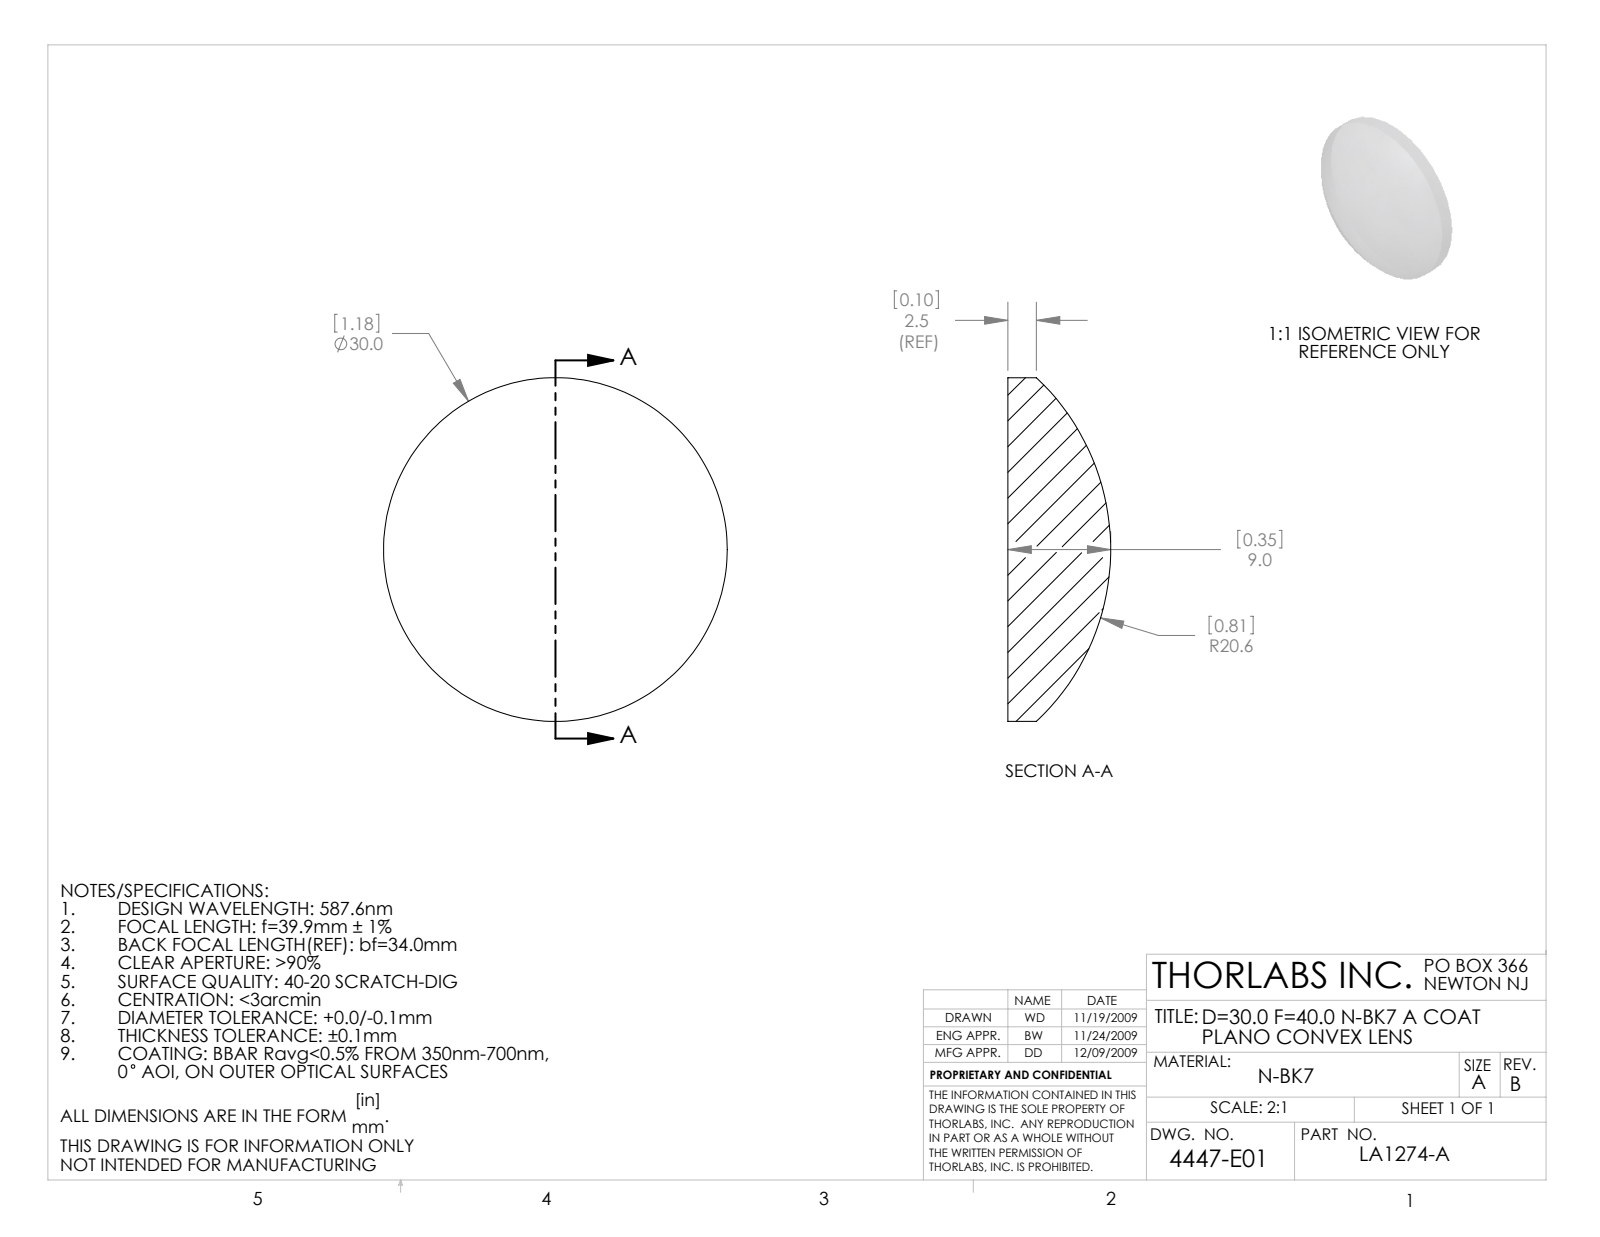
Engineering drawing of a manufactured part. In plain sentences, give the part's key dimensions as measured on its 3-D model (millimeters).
The part is named "4447-E0W". Its 3-D file was written by "SolidWorks 2009 (AUTOMOTIVE_DESIGN)". It is 1 solid with 5 faces: 1 planar, 2 cylindrical and 2 other. Overall it measures 30 by 30 by 8.97 millimeters. Its volume is 4 193 cubic millimeters and its surface area 1 780 square millimeters. Round bosses or shafts: 1 of diameter 30.
